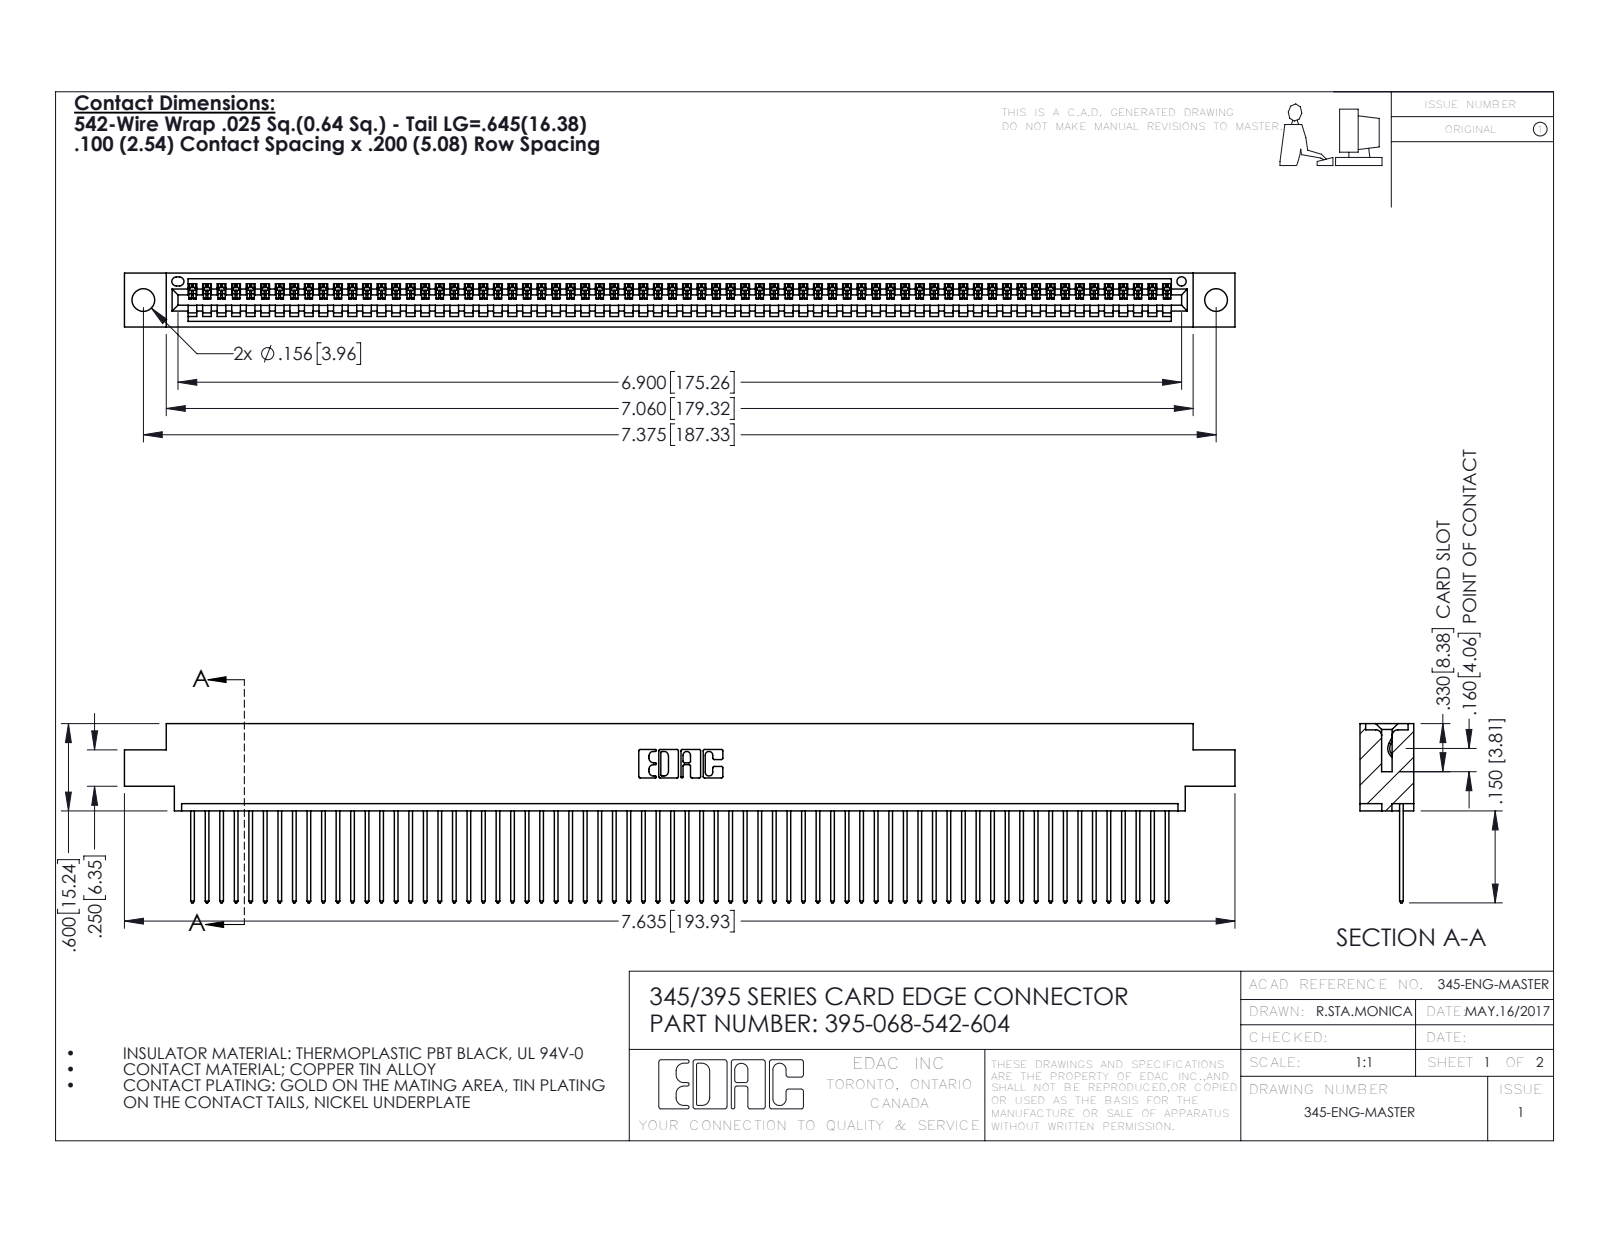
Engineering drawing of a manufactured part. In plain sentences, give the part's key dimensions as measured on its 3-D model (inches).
The part is named "345 Part_0.170 Offset - 0.156 Dia-TH; 395-068-542-604; 345-292-001_345-293-142". Its 3-D file was written by "SolidWorks 2016 (CONFIG_CONTROL_DESIGN)". It is 69 solids with 4074 faces: 2804 planar, 1270 cylindrical and 0 other. Overall it measures 7.635 by 1.232 by 0.37 inches. Its volume is 1.134 cubic inches and its surface area 40.21 square inches. Round holes: 2 of diameter 0.156, 1 of diameter 0.064. Partial cylindrical surfaces (rounded edges, fillets, slot ends): 136 of radius 0.006, 136 of radius 0.01, 22 of radius 0.01, 6 of radius 0.007, 6 of radius 0.031, 3 of radius 0.026, 2 of radius 0.031, 2 of radius 0.04. The main face-to-face distances are 0.072, 0.298, 0.37, 0.098, 0.272, 0.025, 0.2, 0.225, 0.175, 0.149. The hole center spacings are 0.27, 7.139, 7.375.
